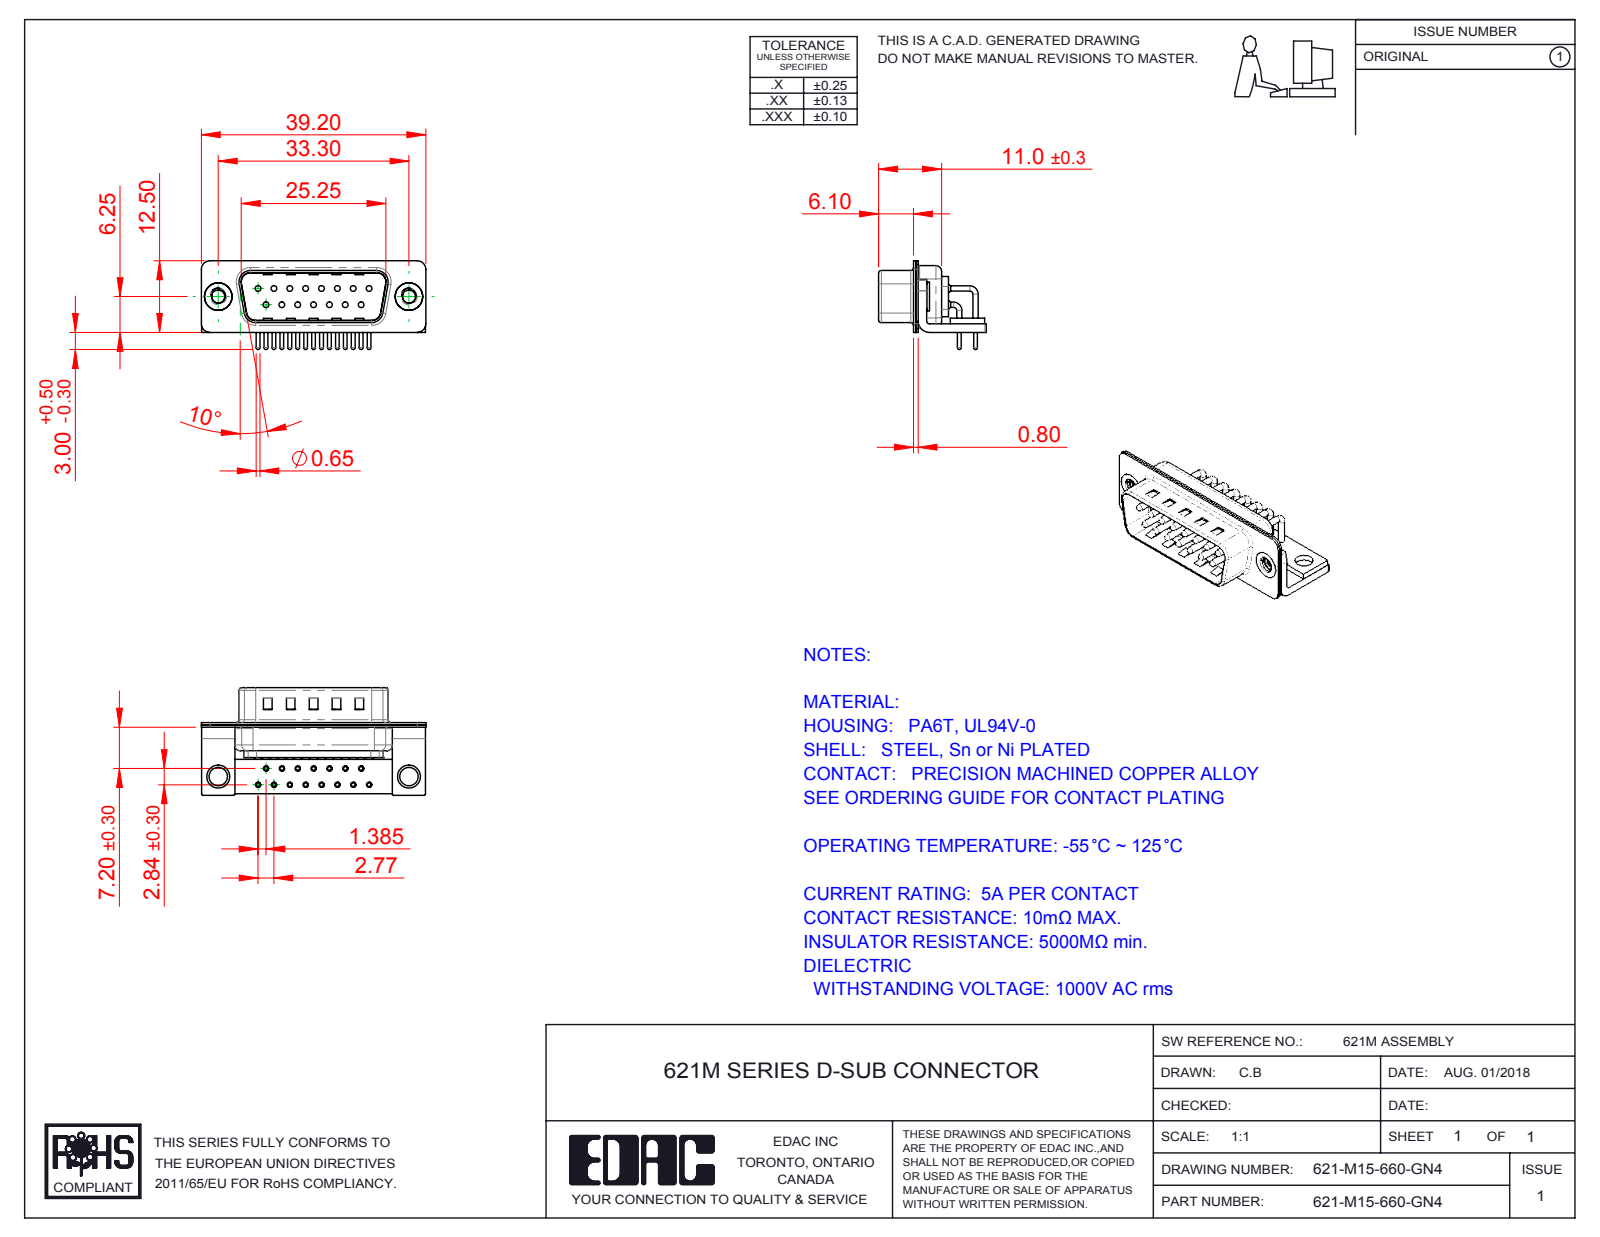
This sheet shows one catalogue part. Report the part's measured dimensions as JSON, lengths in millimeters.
{"part_name": "621M Contact Row 1; 621M Contact Row 2; 621M 4-40 Threaded Rivet_Stabilizer; 621M Stabilizer Bracket (+5 more)", "step_written_by": "SolidWorks 2016 (CONFIG_CONTROL_DESIGN)", "units": "millimeters", "bodies": {"solids": 23, "faces": 2070, "planar": 1125, "cylindrical": 725, "other": 220}, "overall_size": [39.2, 18.8, 15.49], "volume_mm3": 2371, "surface_area_mm2": 6349, "round_holes": [[0.9, 15], [1, 15], [1.7, 15], [2, 15], [2.26, 2], [3.2, 2], [4, 2], [4.8, 2]], "round_bosses_or_shafts": [[0.9, 22], [1.5, 15], [0.65, 15], [5, 2], [4.9, 2]], "partial_cylinders_radius": [[0.25, 16], [1.5, 16], [1.01, 15], [2, 13], [0.5, 9], [1.6, 8], [0.6, 4], [0.65, 4]], "face_to_face_distances": [0.4, 0.85, 1.5, 0.8, 1.25, 10.4, 9.55, 1, 2.1, 1.9], "hole_center_spacings": [3.16, 2.77, 5.54, 8.31, 11.08, 5.03, 5.04, 7.48]}
